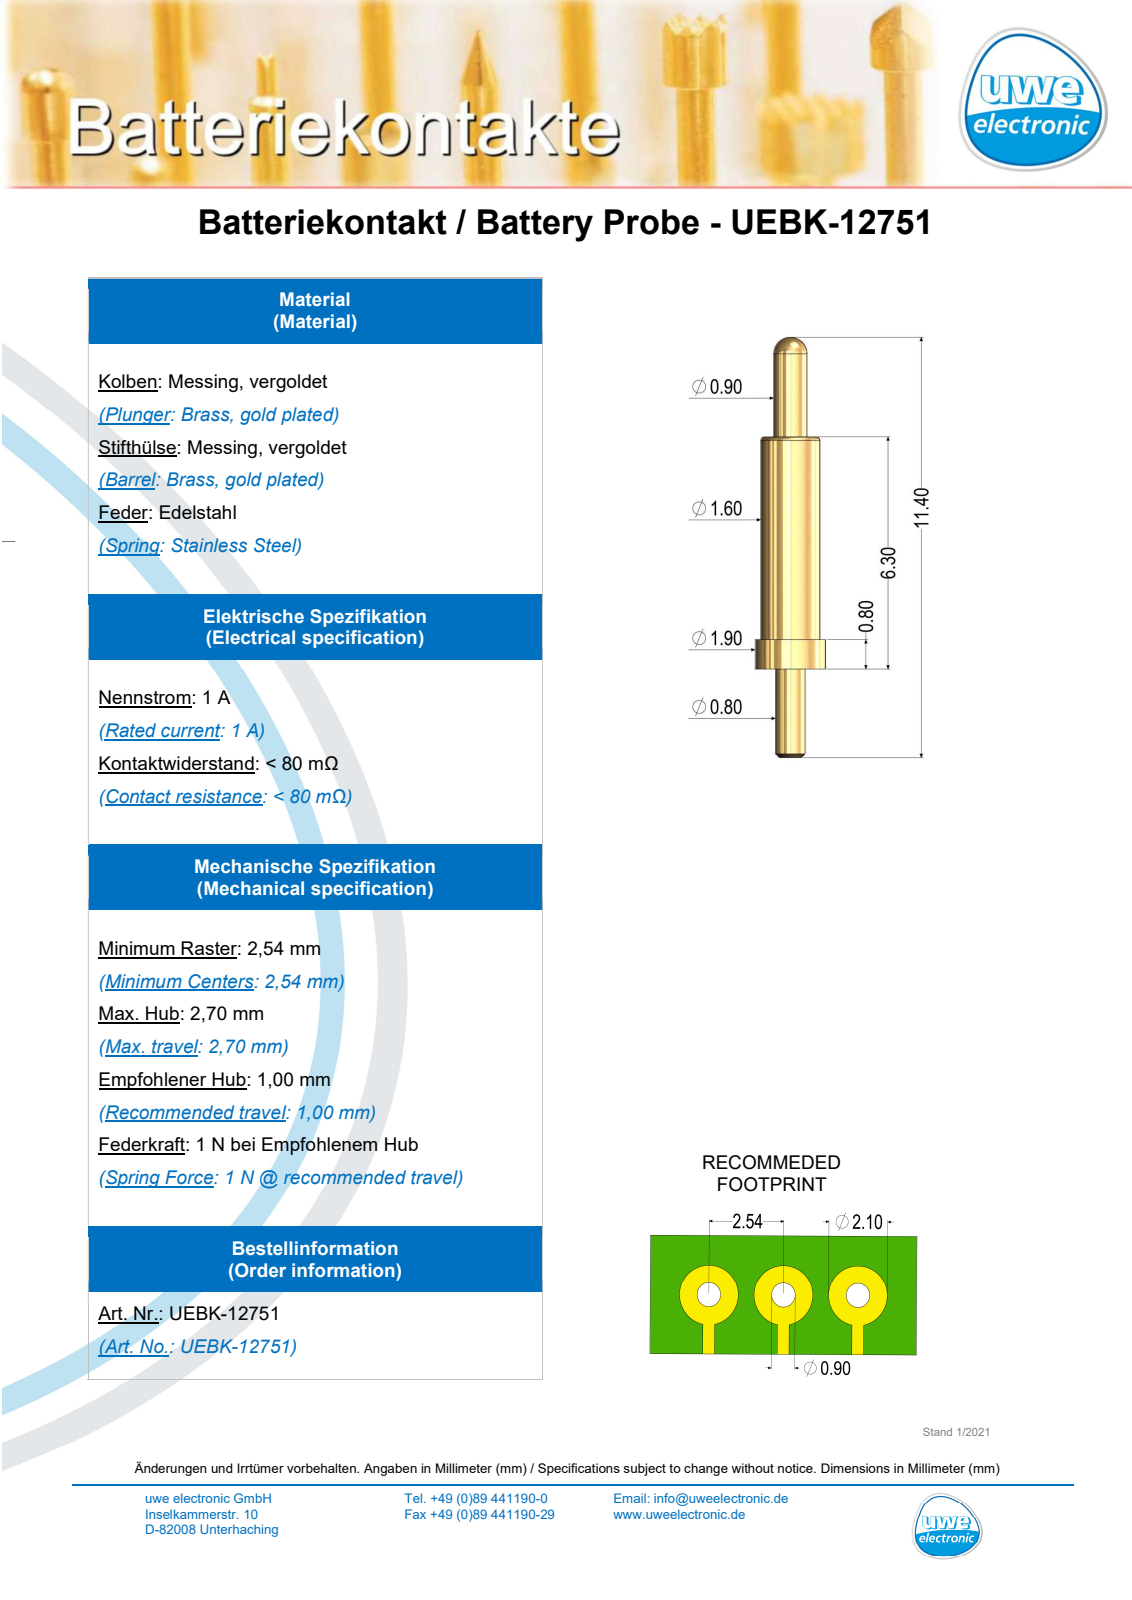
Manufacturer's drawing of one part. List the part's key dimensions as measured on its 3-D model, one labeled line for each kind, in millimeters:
Part name (STEP PRODUCT): UEBK-12751_2017_08_28
STEP written by: SolidWorks 2017 (AUTOMOTIVE_DESIGN)
Units: millimetres
Bodies: 1 solid, 18 faces (4 planar, 8 cylindrical, 6 other)
Overall size (bounding box): 11.4 × 1.9 × 1.9
Volume: 16 mm³ · Surface area: 51 mm²
Round bosses / shafts (diameter × count): ⌀1.9 ×1, ⌀1.6 ×1, ⌀0.9 ×1, ⌀0.8 ×1
Main face-to-face distances: 6.3, 5.5, 0.8, 8.7, 3.2, 2.4
